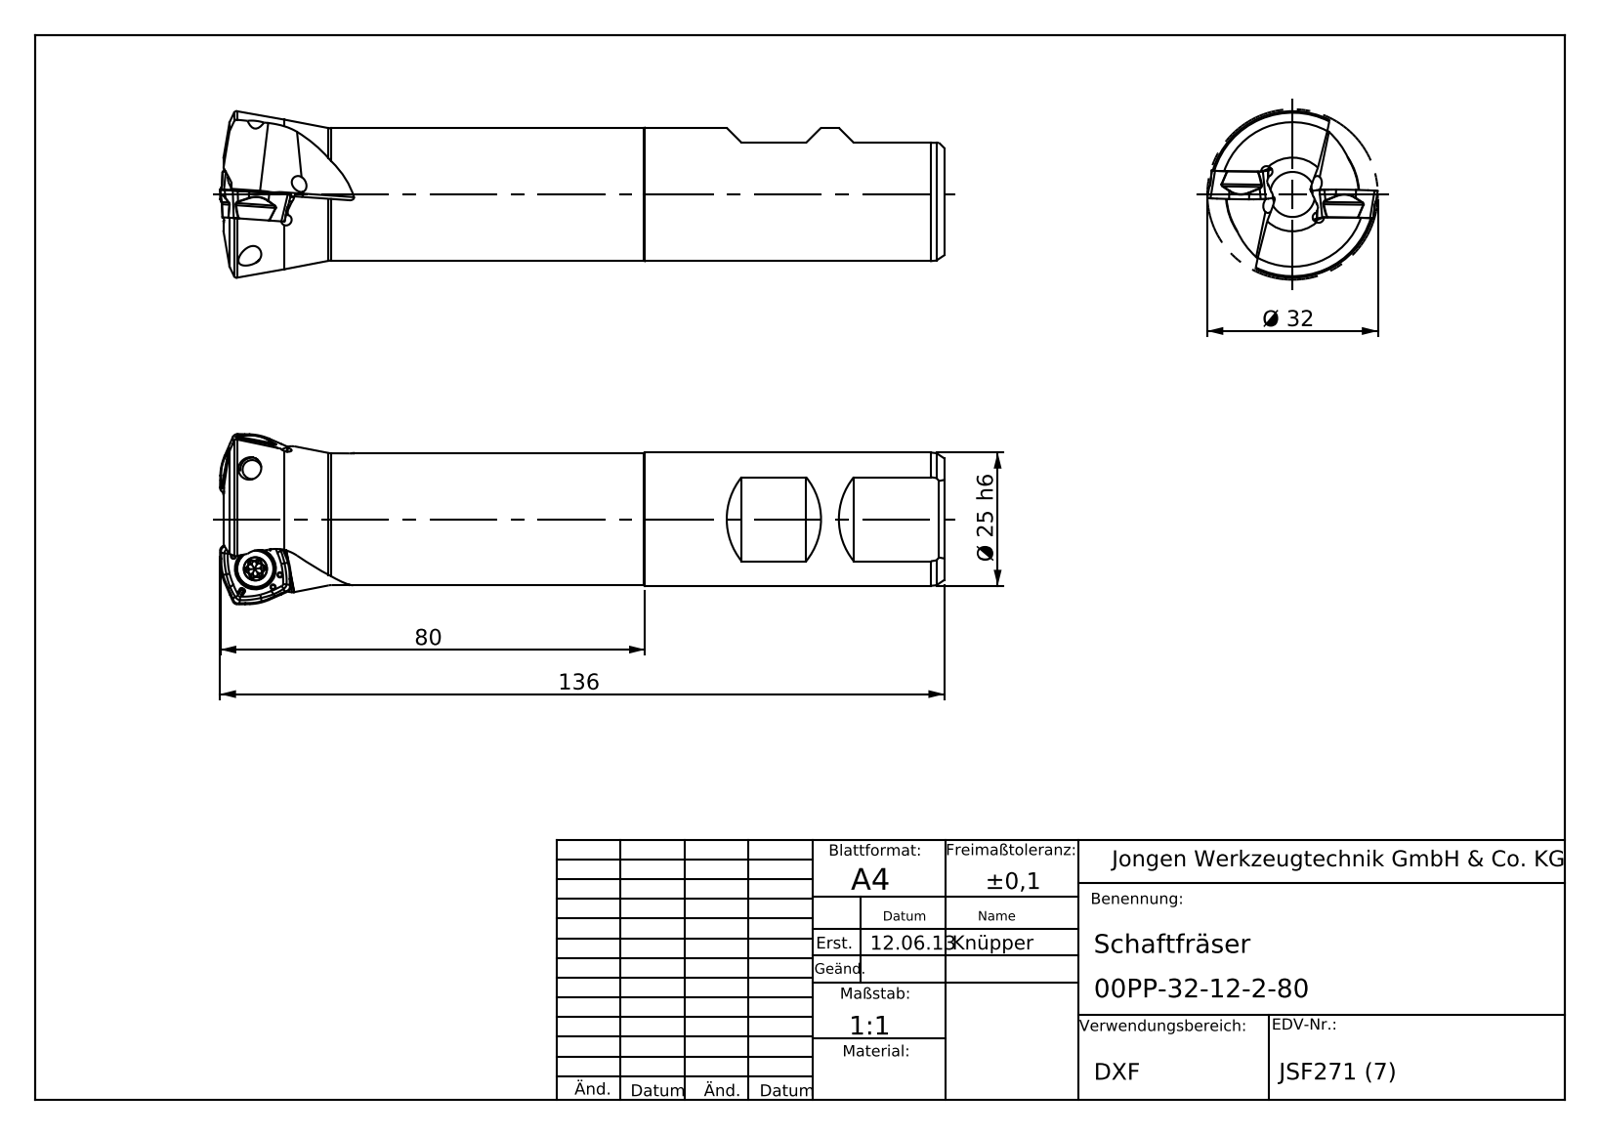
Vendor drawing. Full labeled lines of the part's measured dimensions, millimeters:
Part name (STEP PRODUCT): 00PP-32-12-2-80
STEP written by: SolidWorks 2013 (AUTOMOTIVE_DESIGN)
Units: millimetres
Bodies: 1 solid, 101 faces (44 planar, 23 cylindrical, 34 other)
Overall size (bounding box): 135.95 × 31.97 × 31.97
Volume: 63 234 mm³ · Surface area: 14 839 mm²
Round holes (diameter × count): ⌀3 ×2, ⌀6.5 ×1
Round bosses / shafts (diameter × count): ⌀25 ×1, ⌀24.8 ×1
Partial cylindrical surfaces — rounded edges, fillets, slot ends (radius × count): R0.5 ×4, R1.3 ×4, R1 ×2, R2 ×2
Main face-to-face distances: 133.75, 14.89, 11.31, 26.2, 4.85
